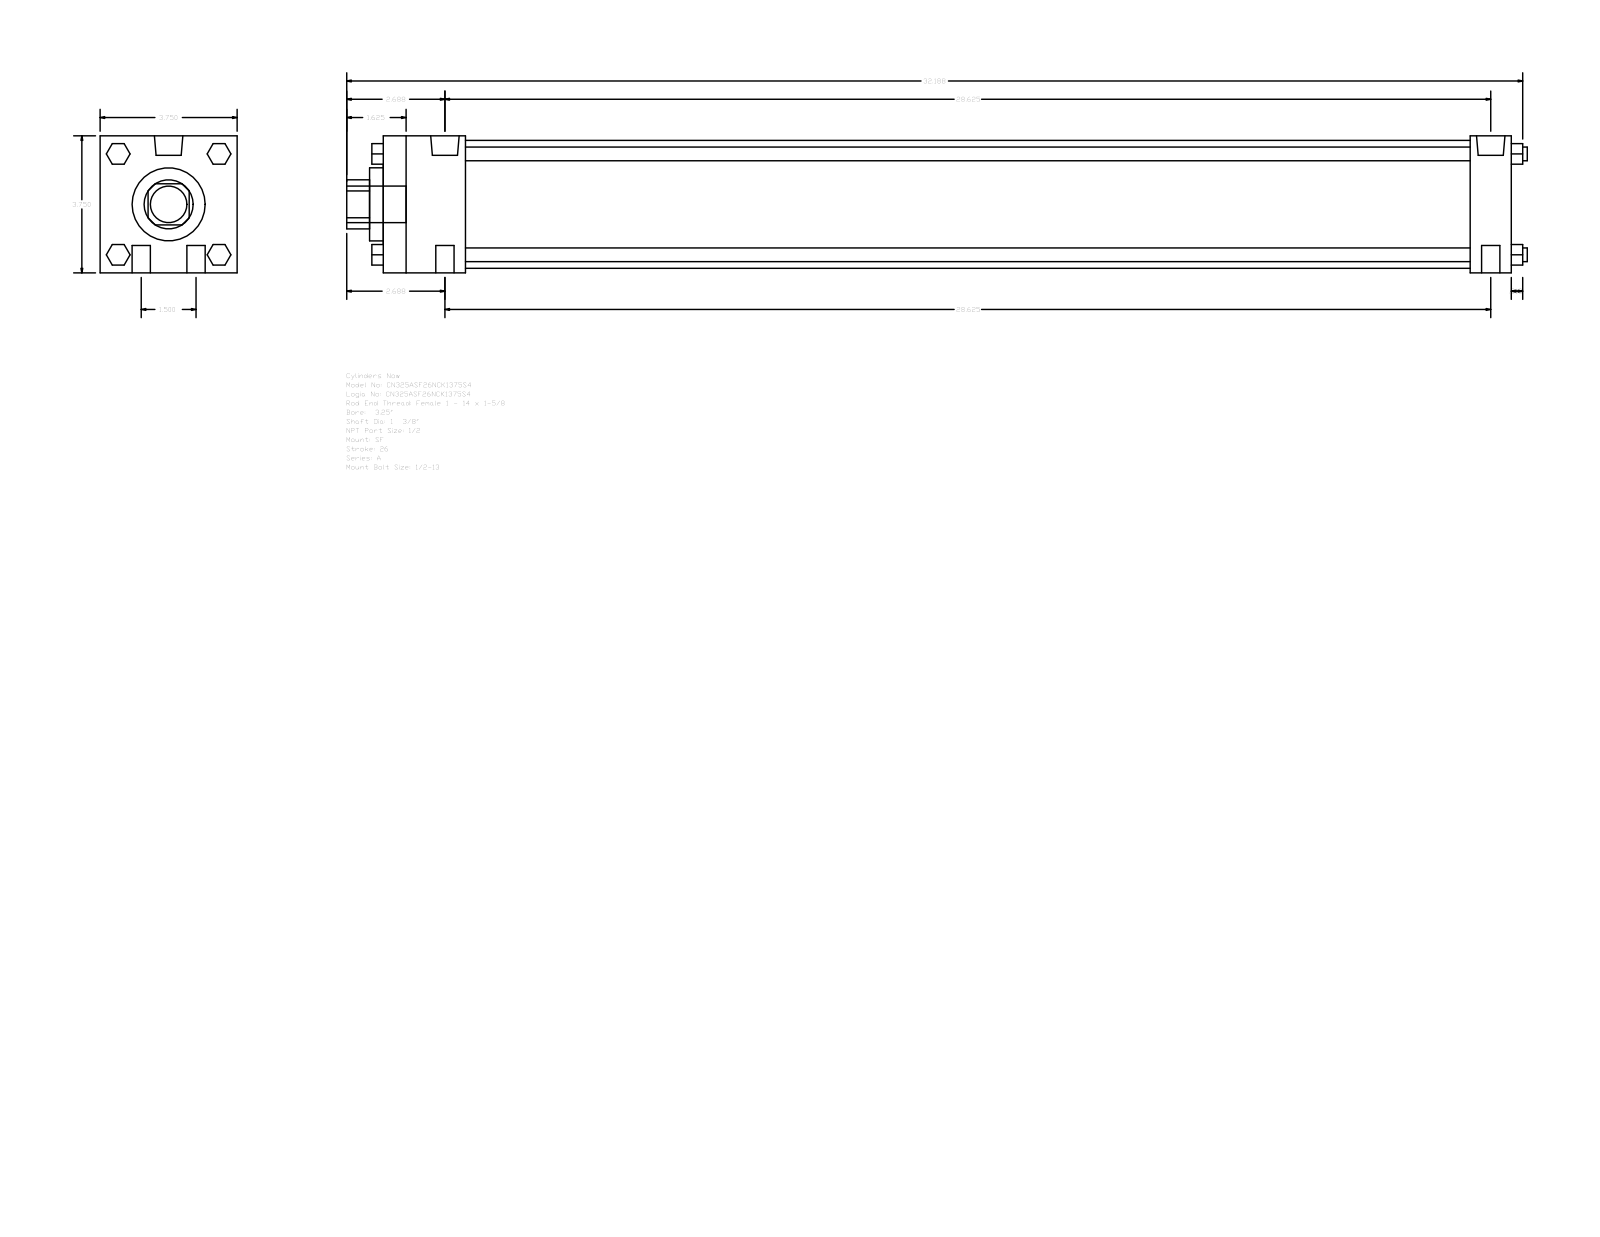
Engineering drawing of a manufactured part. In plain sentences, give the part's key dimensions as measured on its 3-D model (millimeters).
The part is named "A_SF__0325_1.375". Its 3-D file was written by "GSSL Pune (CONFIG_CONTROL_DESIGN)". It is 0 solids with 124 faces: 94 planar, 30 cylindrical and 0 other. Overall it measures 820.74 by 95.25 by 95.25 millimeters. Round holes: 1 of diameter 34.92, 1 of diameter 50.8, 1 of diameter 88.9. Round bosses or shafts: 4 of diameter 12.7, 4 of diameter 9.53, 2 of diameter 19.77, 2 of diameter 8.73, 1 of diameter 25.4. Partial cylindrical surfaces (rounded edges, fillets, slot ends): 1 of radius 17.06. The main face-to-face distances are 95.24, 784.22, 28.57, 755.65, 57.15, 698.5, 727.07, 9.52, 66.67, 765.17.
